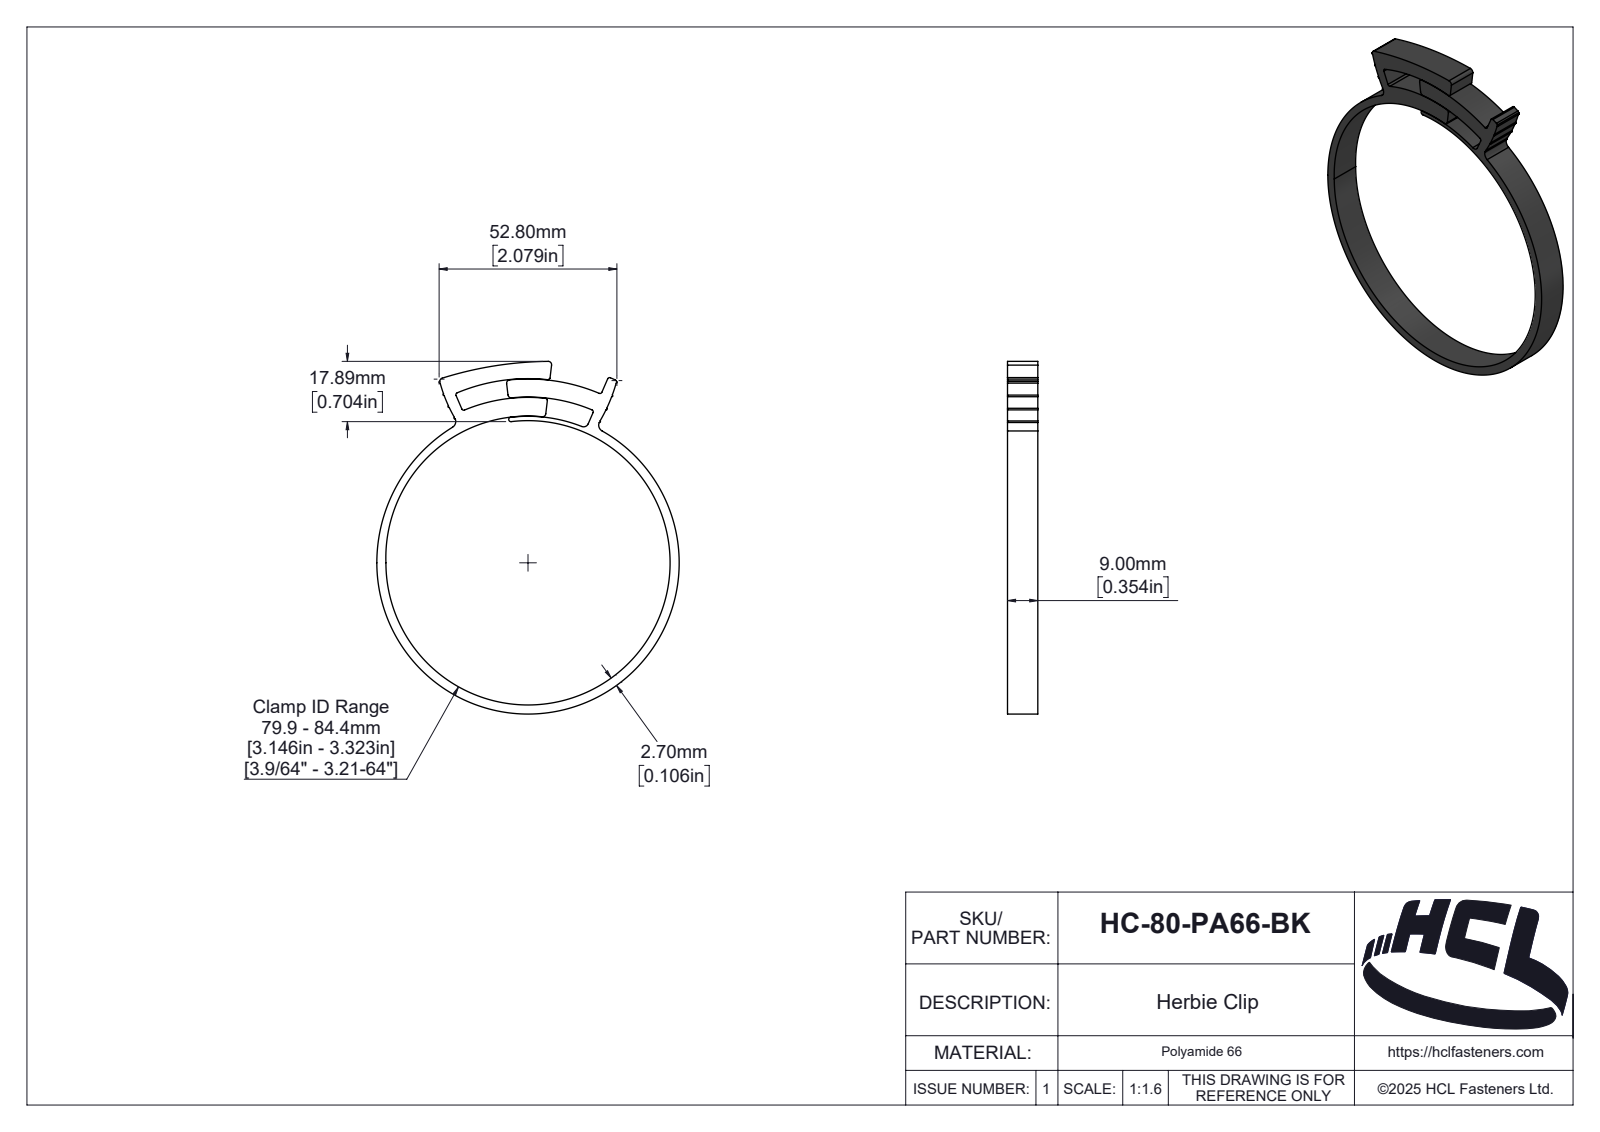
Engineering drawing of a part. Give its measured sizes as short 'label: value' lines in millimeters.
name: HC-80-PA66-BK
written by: SolidWorks 2025 (AUTOMOTIVE_DESIGN)
unit: mm
bodies: 1 solid, 162 faces (13 planar, 100 cylindrical, 49 other)
size: 104.69 × 89.8 × 9
volume: 10 651 mm³; area: 9 096 mm²
rounds: 8× R0.25, 6× R0.6, 5× R1, 2× R2, 1× R0.17, 1× R0.65, 1× R0.67, 1× R0.84
face distances: 9
